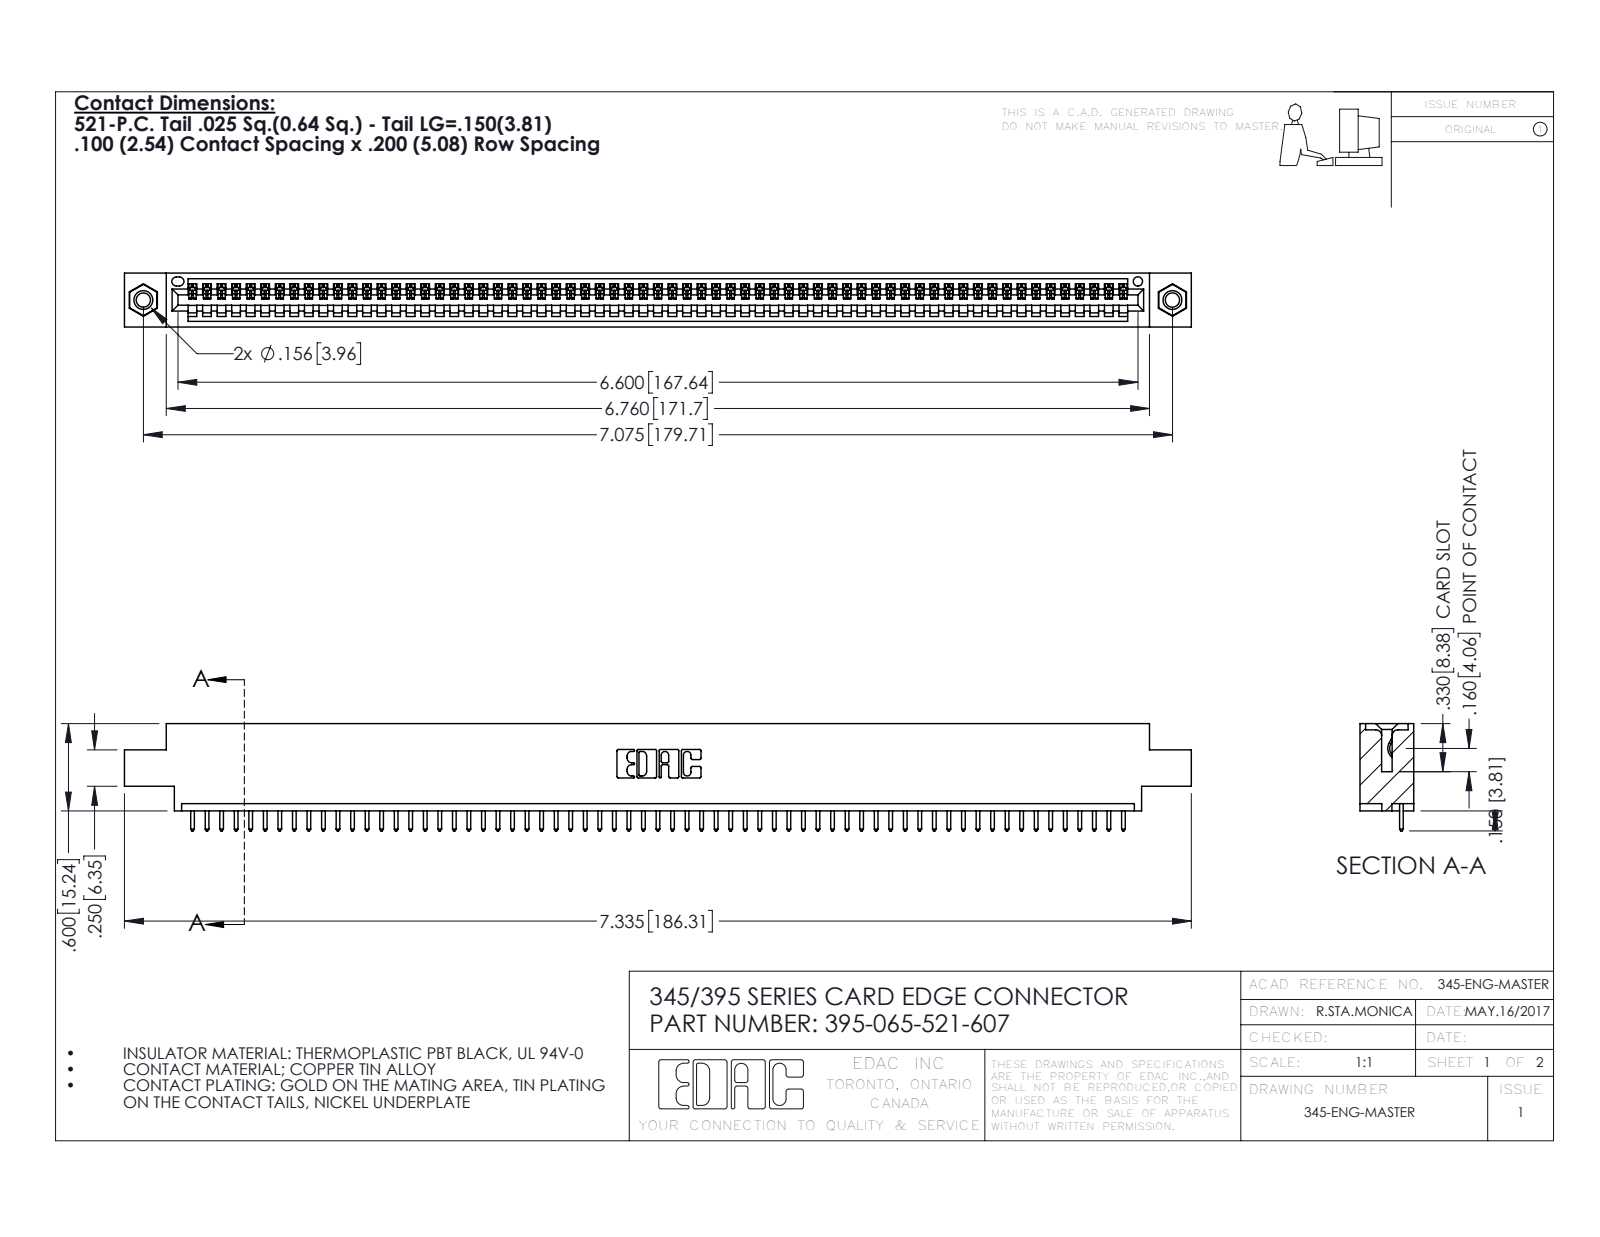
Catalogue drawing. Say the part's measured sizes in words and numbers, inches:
The part is named "345-250-001_345-250-005-103; 395-065-521-607; 345-292-001_345-293-121; 345 Part_0.170 Offset - 0.156 Dia-TI". Its 3-D file was written by "SolidWorks 2016 (CONFIG_CONTROL_DESIGN)". It is 68 solids with 3960 faces: 2716 planar, 1228 cylindrical and 16 other. Overall it measures 7.335 by 0.737 by 0.37 inches. Its volume is 1.072 cubic inches and its surface area 35.81 square inches. Round holes: 2 of diameter 0.098, 2 of diameter 0.125, 2 of diameter 0.156, 1 of diameter 0.064. Round bosses or shafts: 2 of diameter 0.155. Partial cylindrical surfaces (rounded edges, fillets, slot ends): 130 of radius 0.006, 130 of radius 0.01, 22 of radius 0.01, 6 of radius 0.007, 6 of radius 0.031, 3 of radius 0.026, 2 of radius 0.031, 2 of radius 0.04. The main face-to-face distances are 0.072, 0.298, 0.37, 0.2, 0.098, 0.272, 0.025, 0.225, 0.175, 0.149. The hole center spacings are 0.27, 6.839, 7.075.
